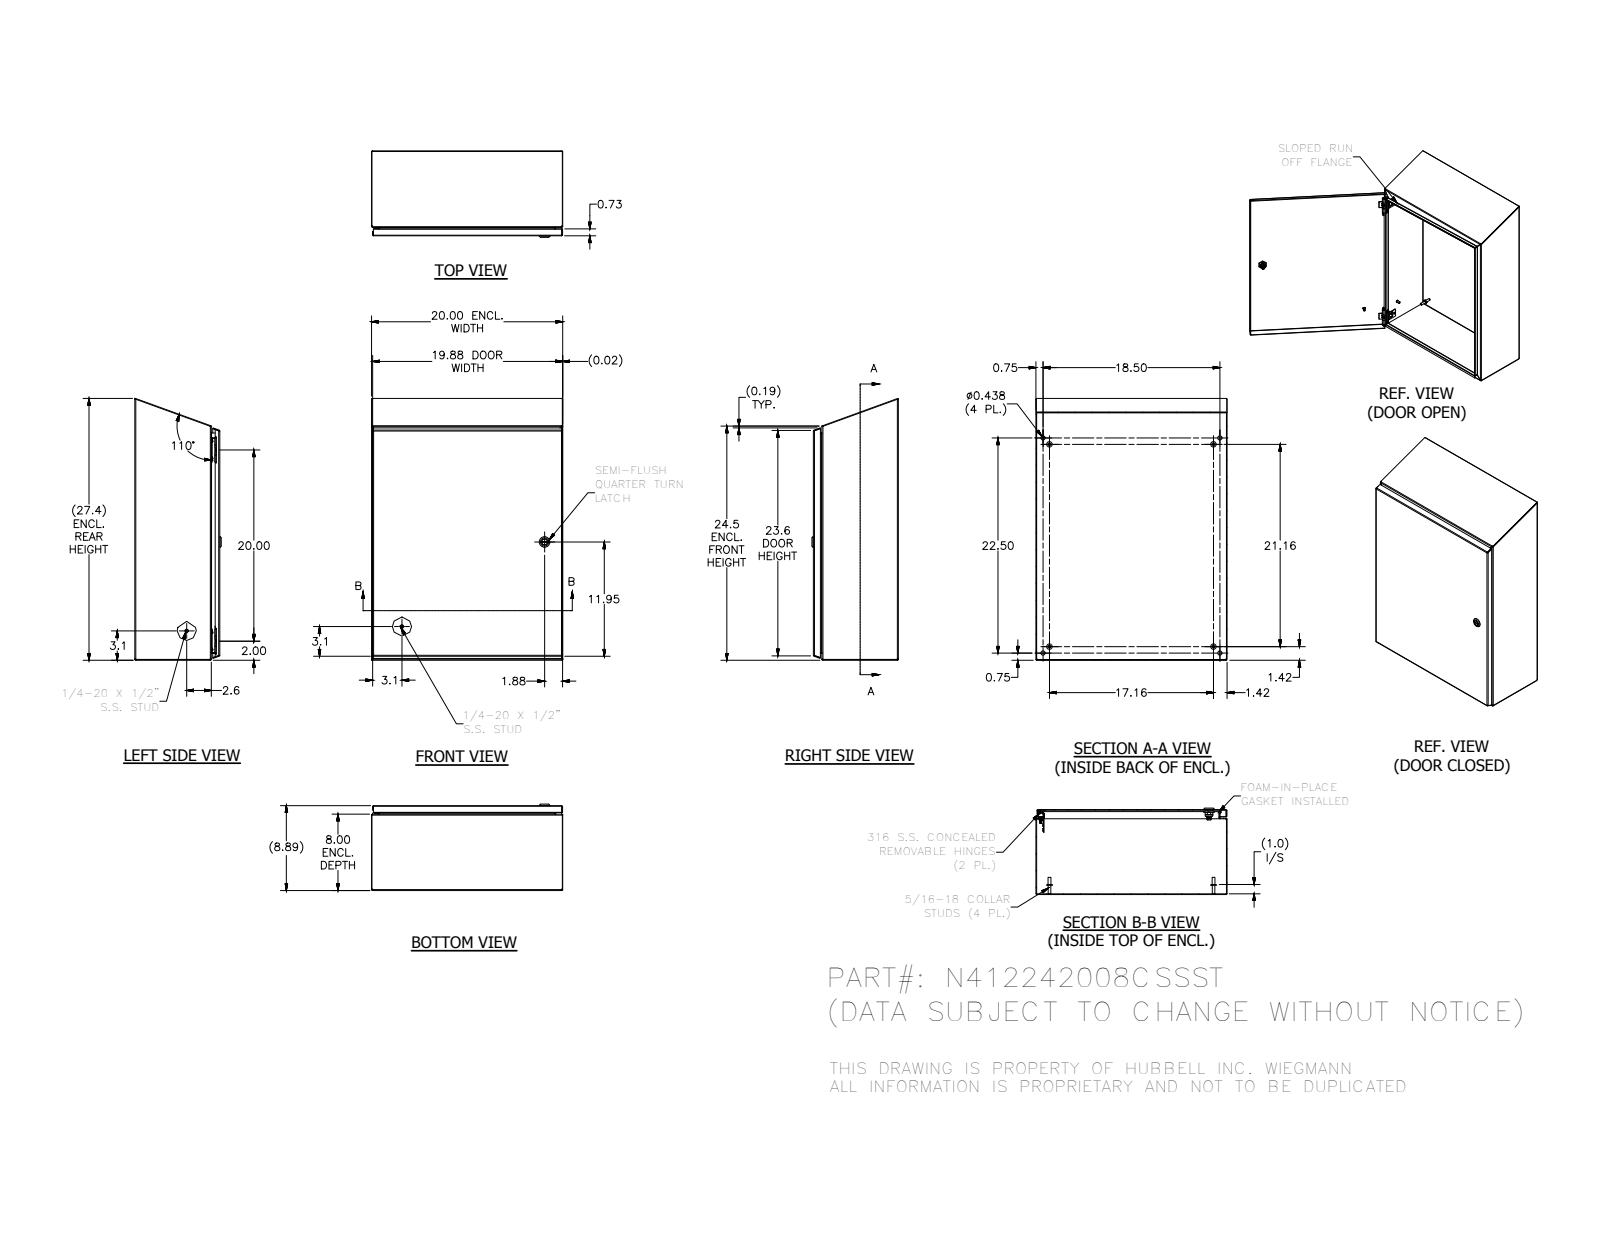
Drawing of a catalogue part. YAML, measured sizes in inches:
part_name: "N412242008CSSST"
step_written_by: "SolidWorks 2018 (AUTOMOTIVE_DESIGN)"
units: inches
bodies: {solids: 36, faces: 1426, planar: 538, cylindrical: 509, other: 379}
overall_size: [27.391, 20, 9.044]
volume: 144.7
surface_area: 3935
round_holes:
  - {diameter: 0.093, count: 4}
  - {diameter: 0.152, count: 4}
  - {diameter: 0.167, count: 4}
  - {diameter: 0.172, count: 4}
  - {diameter: 0.187, count: 4}
  - {diameter: 0.437, count: 4}
  - {diameter: 0.156, count: 3}
  - {diameter: 0.187, count: 1}
  - {diameter: 0.197, count: 1}
  - {diameter: 0.315, count: 1}
  - {diameter: 0.394, count: 1}
  - {diameter: 0.402, count: 1}
round_bosses_or_shafts:
  - {diameter: 0.25, count: 10}
  - {diameter: 0.563, count: 4}
  - {diameter: 0.36, count: 4}
  - {diameter: 0.32, count: 4}
  - {diameter: 0.3, count: 4}
  - {diameter: 0.275, count: 4}
  - {diameter: 0.256, count: 4}
  - {diameter: 0.164, count: 4}
partial_cylinders:
  - {radius: 0.031, count: 29}
  - {radius: 0.05, count: 26}
  - {radius: 0.105, count: 19}
  - {radius: 0.016, count: 18}
  - {radius: 0.02, count: 16}
  - {radius: 0.125, count: 16}
  - {radius: 0.032, count: 8}
  - {radius: 0.524, count: 6}
face_to_face_distances: [0.074, 8.813, 8.739, 8.887, 19.926, 20, 19.852, 7.926, 0.887, 0.813]
hole_center_spacings: [20, 0.5, 0.656, 0.66, 0.952, 1.307, 1.311, 1.599]
